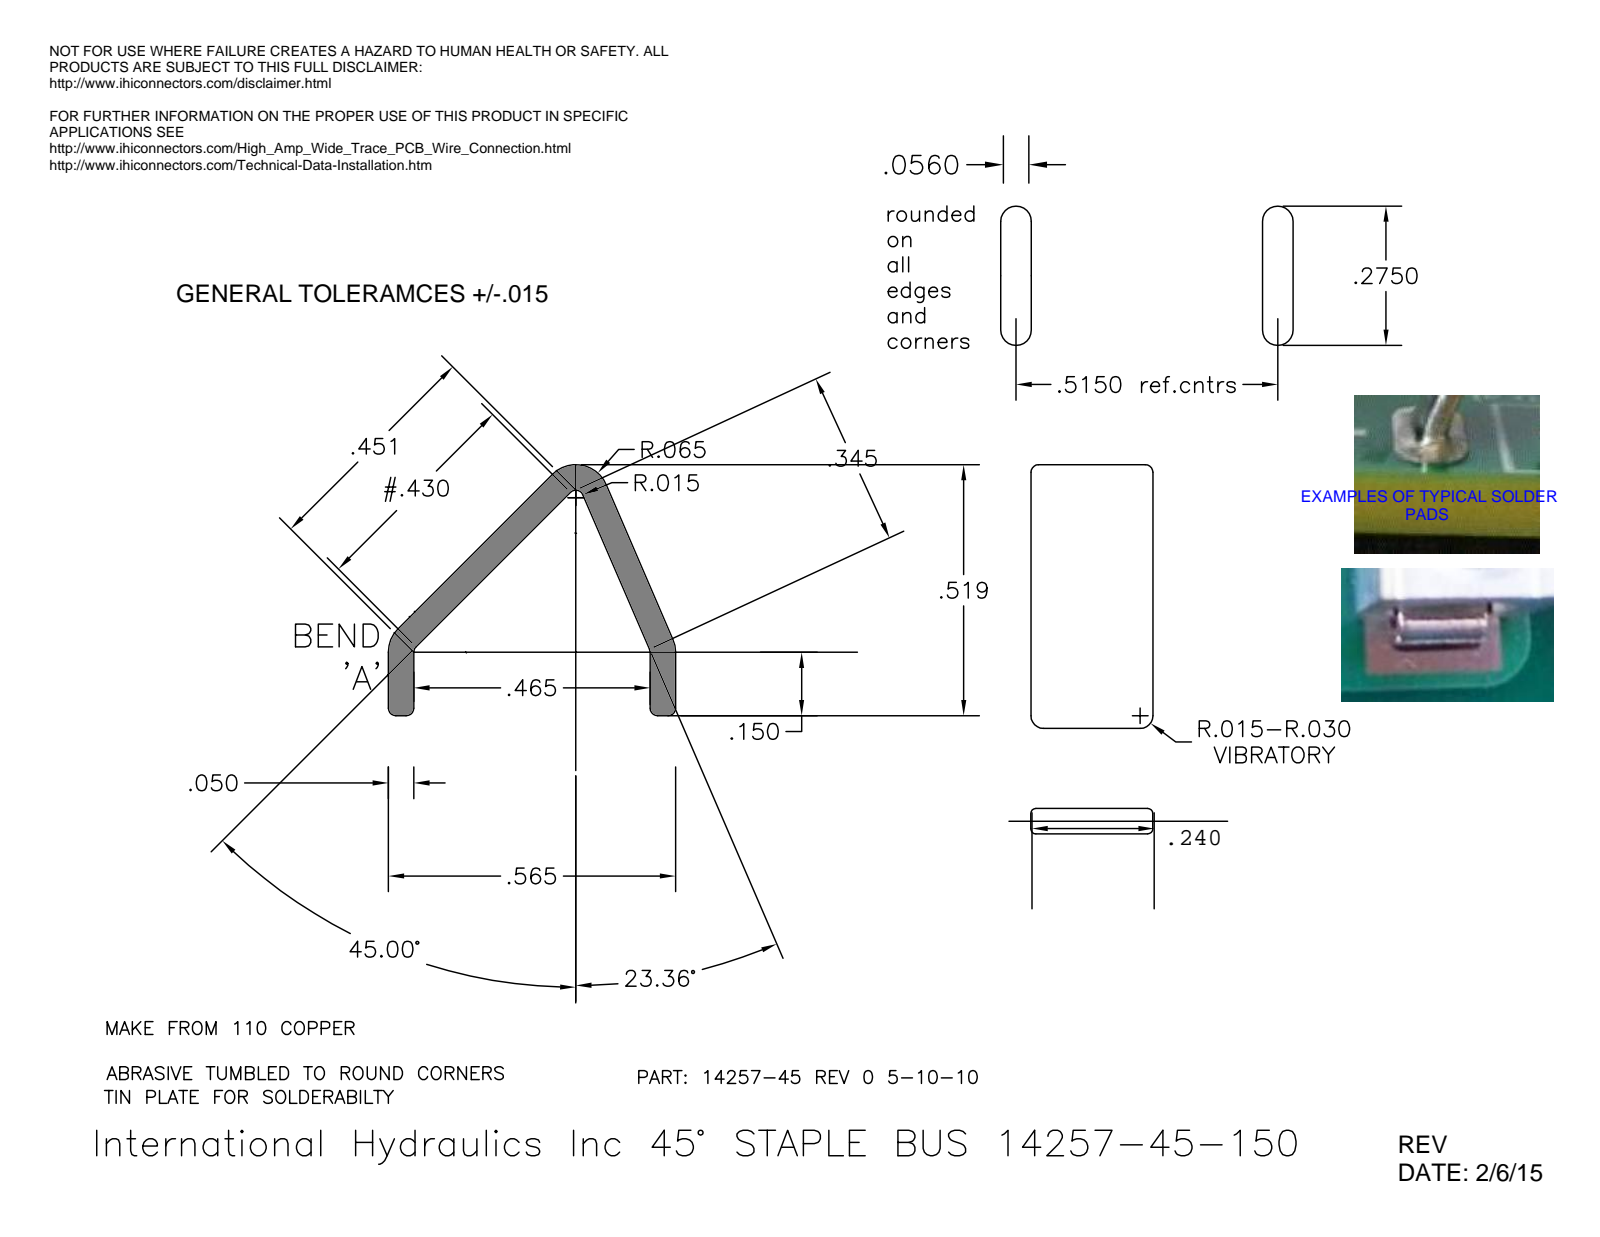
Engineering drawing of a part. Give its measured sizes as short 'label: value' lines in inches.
name: 14257-45-150
written by: Autodesk Inventor 2015 (AUTOMOTIVE_DESIGN)
unit: in
bodies: 1 solid, 62 faces (12 planar, 30 cylindrical, 20 other)
size: 0.565 × 0.519 × 0.245
volume: 0.014 in³; area: 0.699 in²
rounds: 22× R0.01, 3× R0.015, 3× R0.065
face distances: 0.05, 0.515, 0.245, 0.565, 0.465
